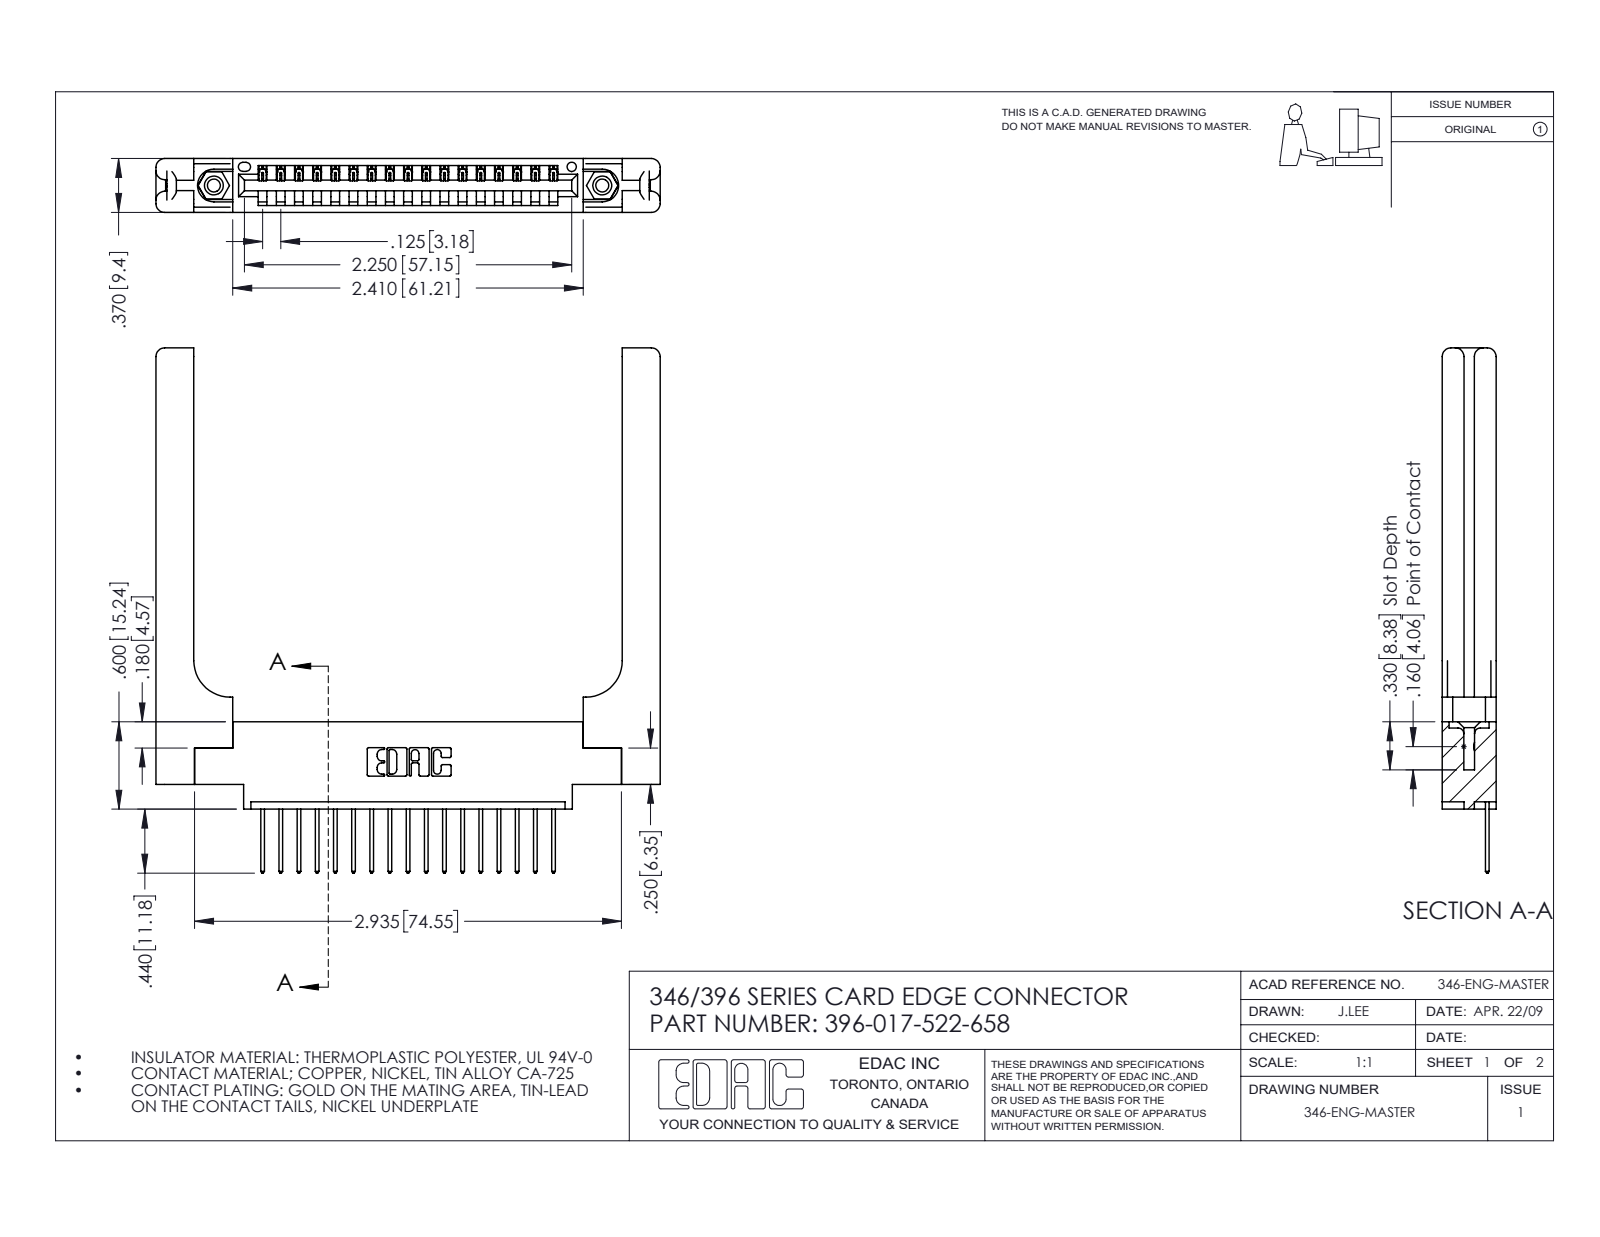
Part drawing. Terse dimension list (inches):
name: 345-250-001_345-250-001-102; 346 Part_0.170 Offset - 0.156 Dia-TH; 345-292-001_345-293-122; 396-017-522-658 (+1 more)
written by: SolidWorks 2016 (CONFIG_CONTROL_DESIGN)
unit: in
bodies: 22 solids, 1368 faces (908 planar, 400 cylindrical, 60 other)
size: 3.61 × 3.466 × 0.37
volume: 0.953 in³; area: 23.64 in²
holes: 2× ⌀0.089, 2× ⌀0.125, 2× ⌀0.156, 1× ⌀0.064
bosses: 2× ⌀0.155
rounds: 34× R0.006, 34× R0.01, 22× R0.01, 16× R0.06, 6× R0.007, 6× R0.031, 3× R0.026, 2× R0.03
face distances: 0.37, 0.072, 0.15, 0.148, 0.048, 0.322, 0.25, 0.102, 0.22, 0.173
hole spacings: 0.246, 2.463, 2.67
